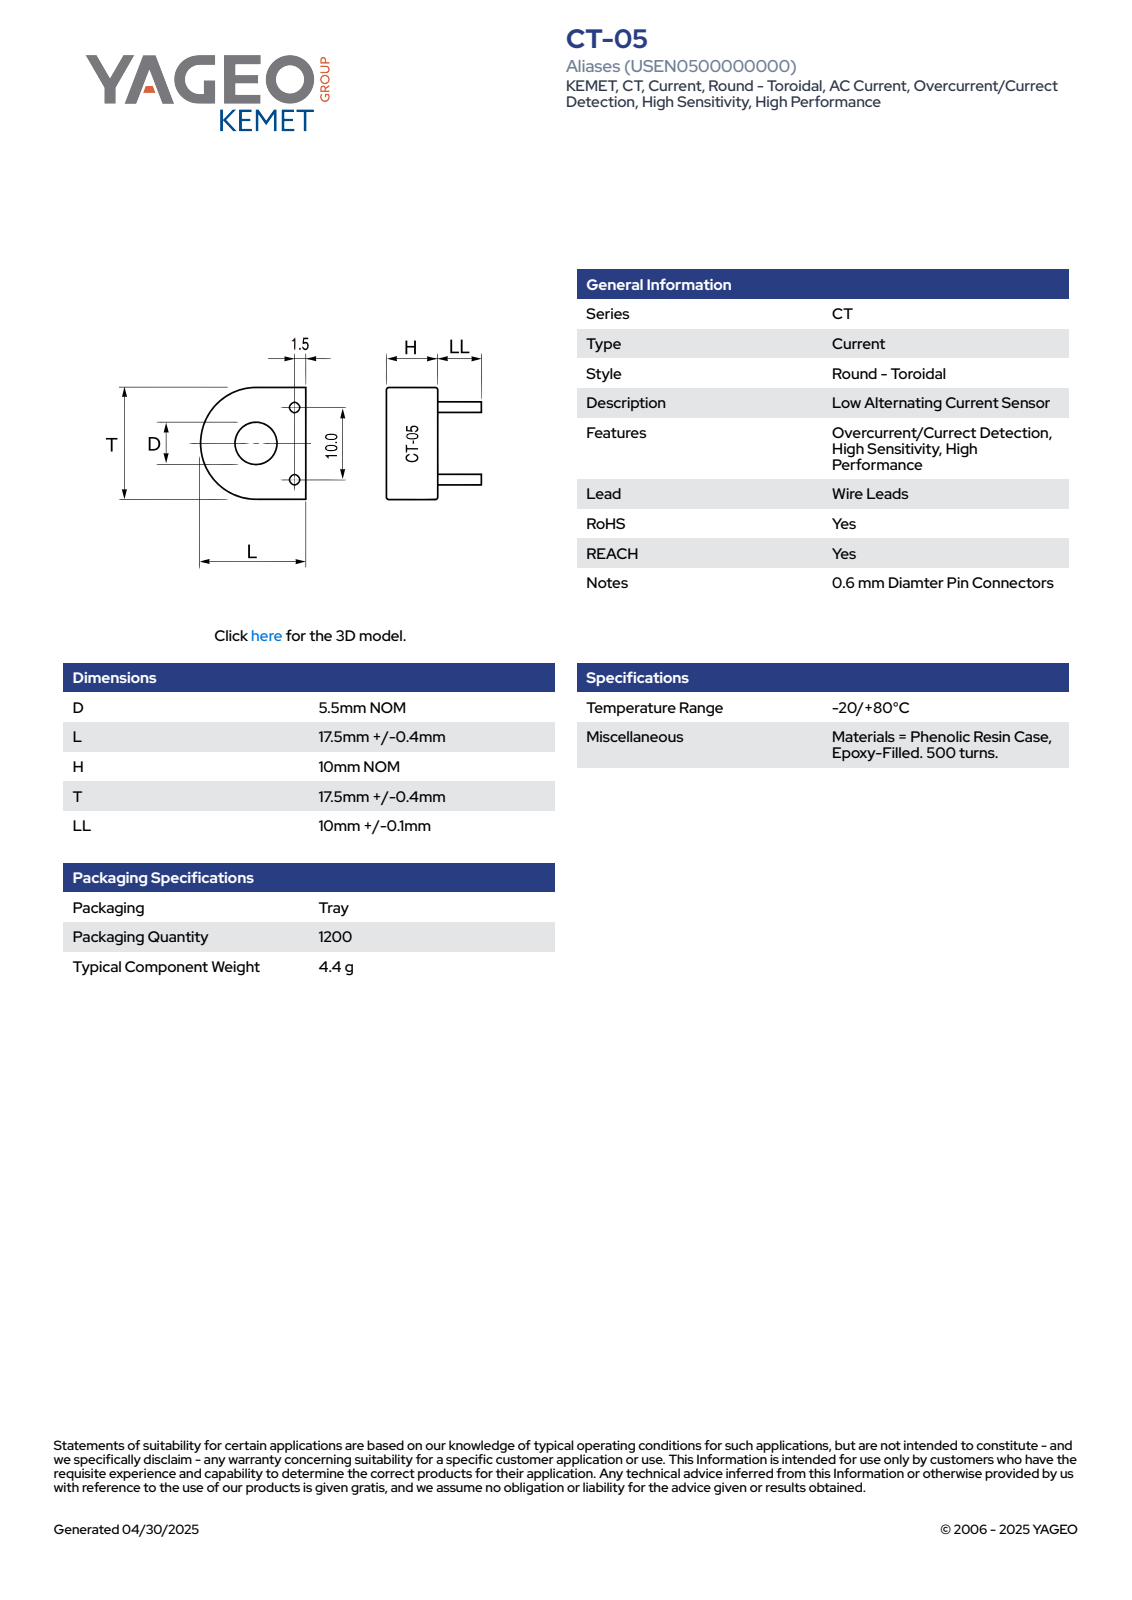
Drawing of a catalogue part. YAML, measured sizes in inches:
part_name: "SC_CT05_D5.5L17.9H11T17.9LL10.1"
step_written_by: "SolidWorks 2014 (AUTOMOTIVE_DESIGN)"
units: inches
bodies: {solids: 1, faces: 82, planar: 31, cylindrical: 18, other: 33}
overall_size: [0.831, 0.705, 0.705]
volume: 0.177
surface_area: 2.303
round_holes:
  - {diameter: 0.217, count: 1}
round_bosses_or_shafts:
  - {diameter: 0.047, count: 2}
partial_cylinders:
  - {radius: 0.008, count: 4}
  - {radius: 0.352, count: 1}
  - {radius: 0.353, count: 1}
face_to_face_distances: [0.433, 0.705, 0.398, 0.831, 0.177, 0.256, 0.654, 0.574, 0.08, 0.192]
